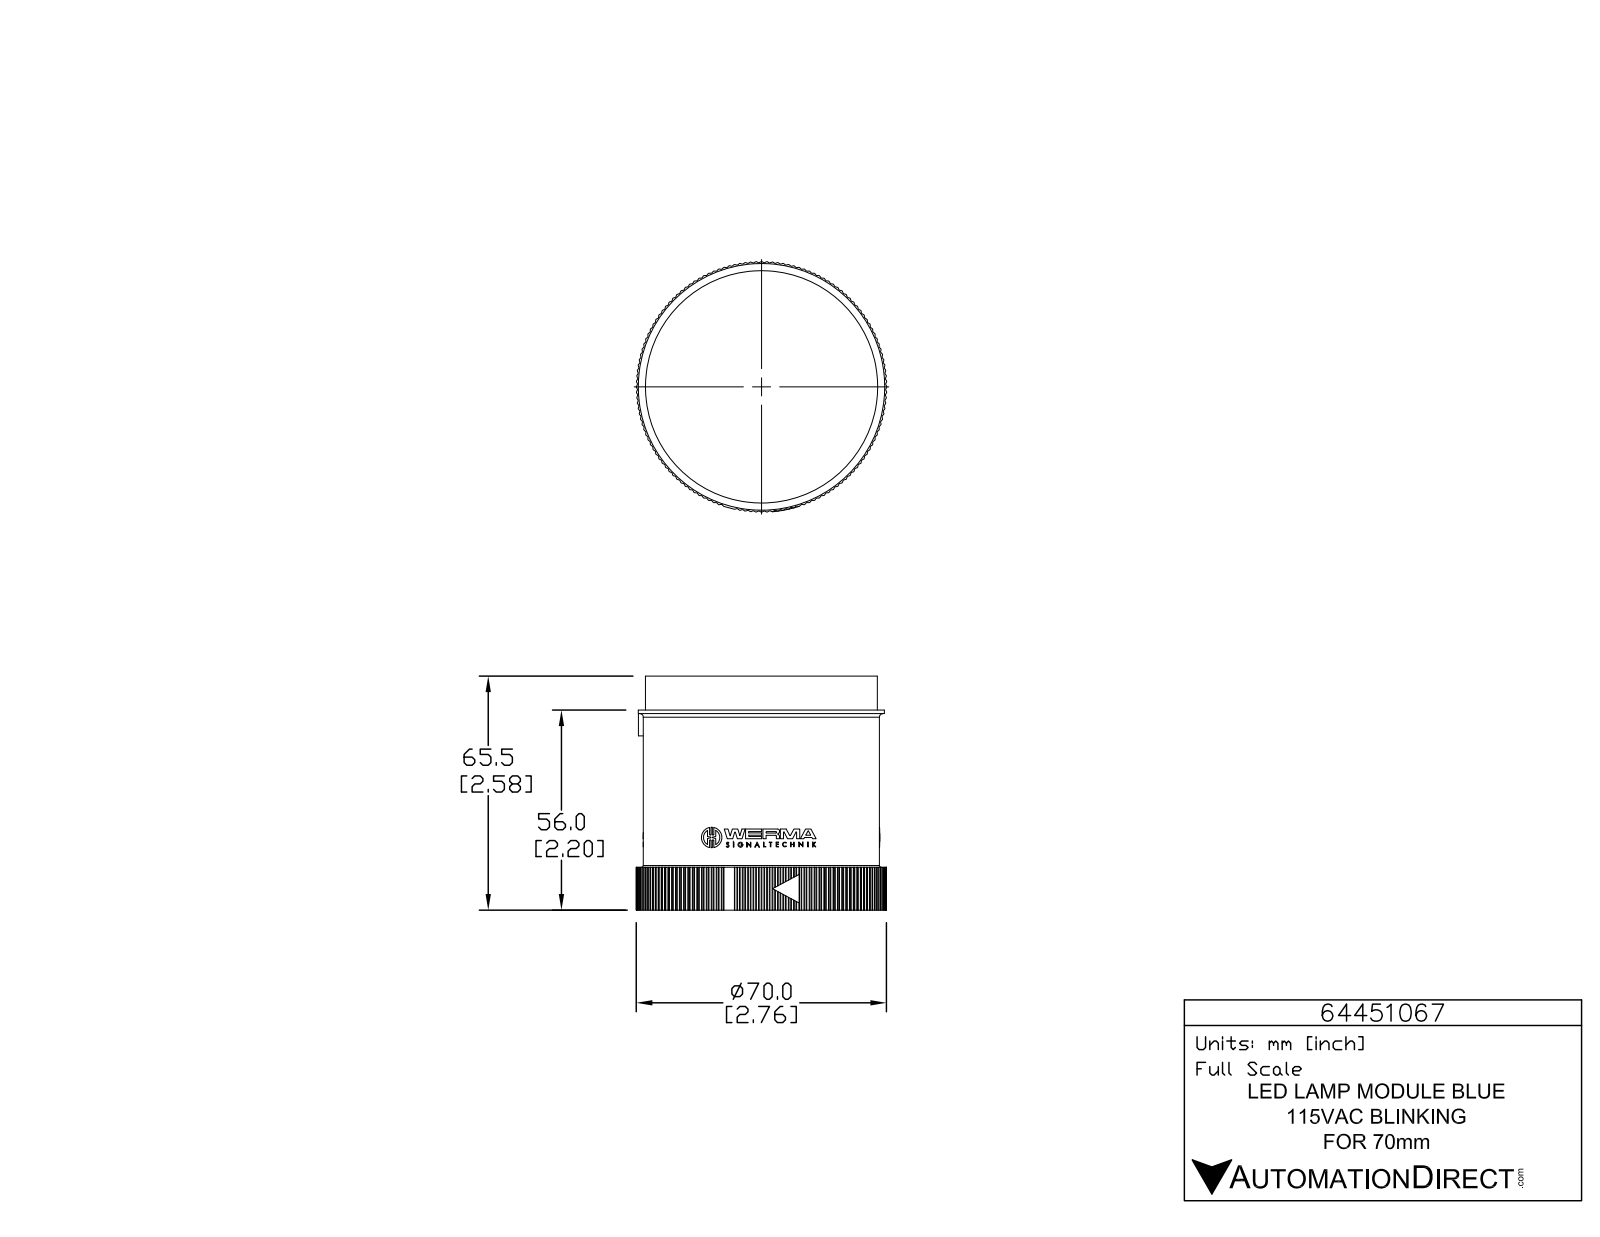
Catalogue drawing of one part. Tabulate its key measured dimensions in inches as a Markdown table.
| quantity | value |
| --- | --- |
| part name | 64451067 |
| STEP written by | SolidWorks 2015 (AUTOMOTIVE_DESIGN) |
| units | inches |
| bodies | 1 solid, 1400 faces (832 planar, 563 cylindrical, 5 other) |
| overall size | 2.762 × 2.762 × 2.579 |
| volume | 12.02 in³ |
| surface area | 37.48 in² |
| round holes (diameter × count) | 0.039 × 3, 2.575 × 1 |
| round bosses / shafts (diameter × count) | 0.226 × 3, 0.056 × 3, 2.717 × 1, 2.606 × 1, 2.559 × 1 |
| partial cylindrical surfaces (radius × count) | 0.008 × 285, 0.008 × 6, 0.008 × 6, 0.008 × 6, 0.131 × 6, 0.004 × 3, 0.005 × 3, 0.008 × 3 |
| main face-to-face distances | 2.201, 2.451, 0.378, 2.579, 2.205, 1.827, 0.374, 2.452, 0.472, 0.094 |
